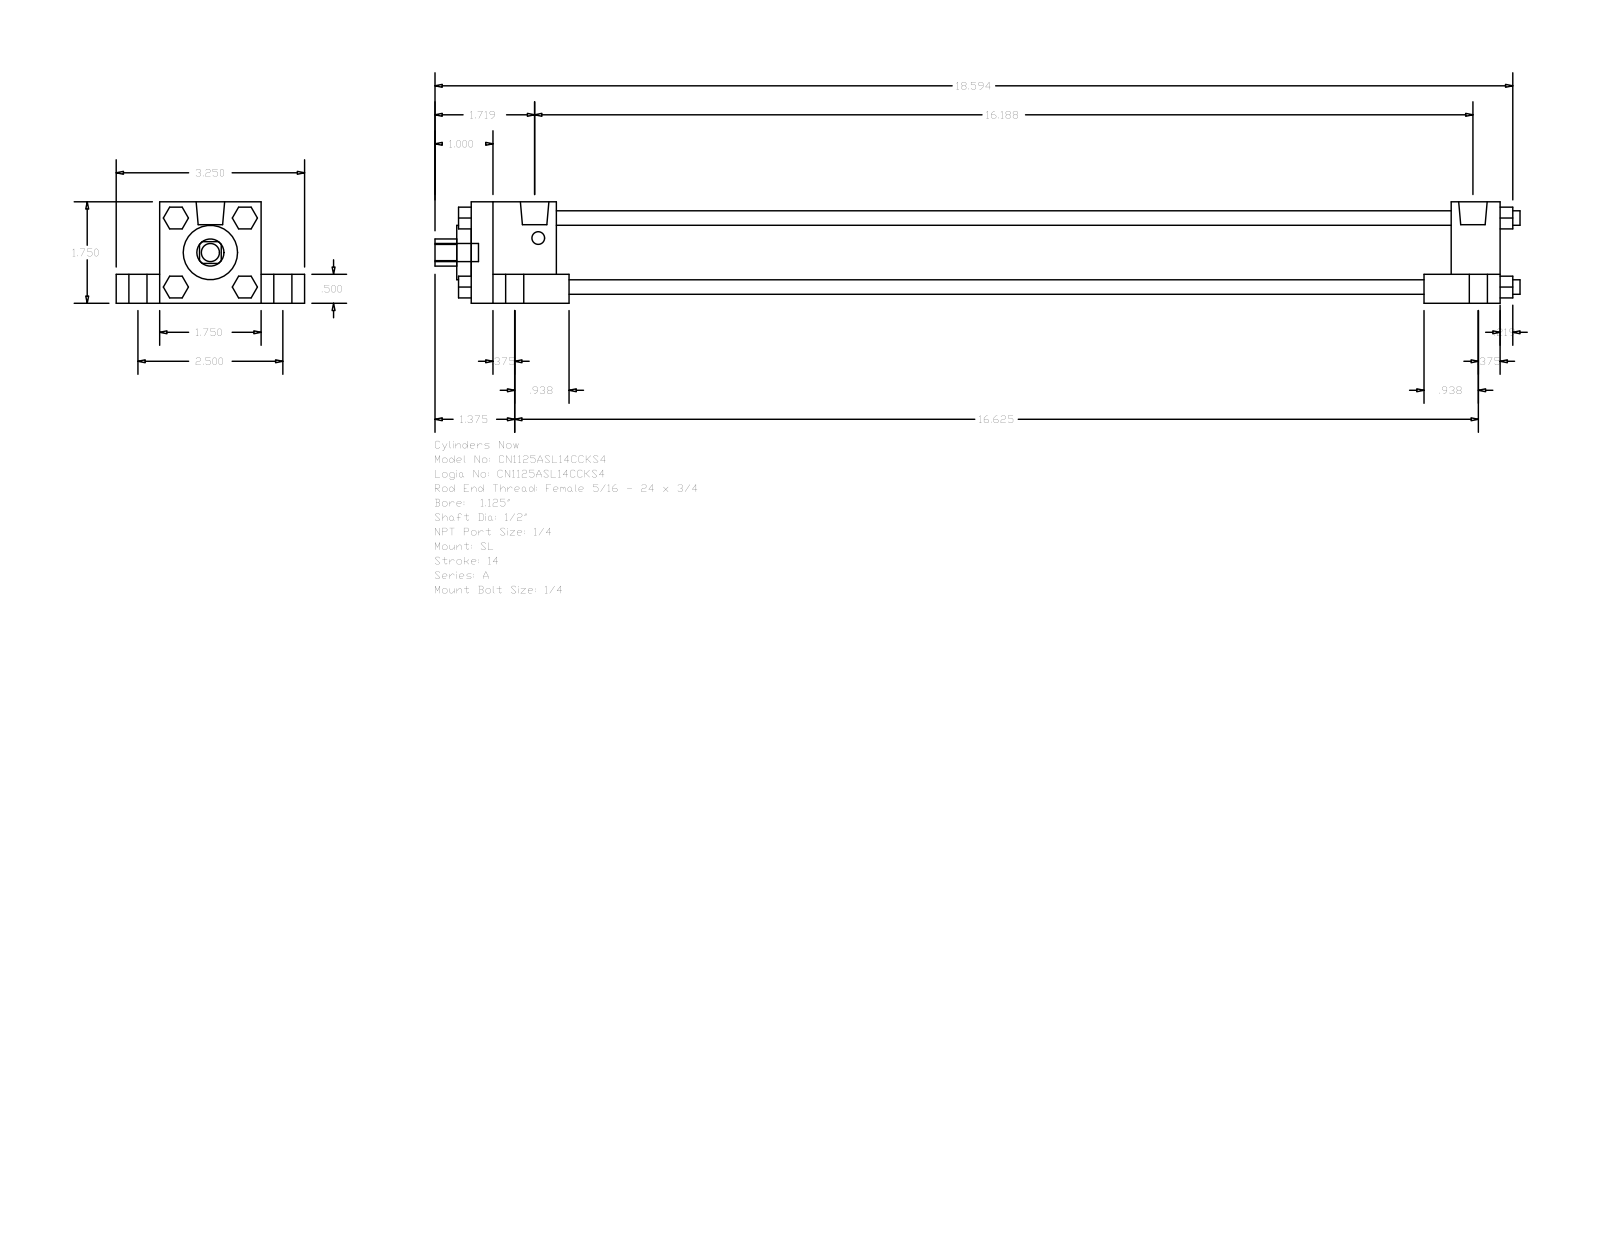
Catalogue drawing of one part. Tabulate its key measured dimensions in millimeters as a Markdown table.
| quantity | value |
| --- | --- |
| part name | A_SL__0112_0.5 |
| STEP written by | GSSL Pune (CONFIG_CONTROL_DESIGN) |
| units | millimeters |
| bodies | 0 solids, 150 faces (114 planar, 36 cylindrical, 0 other) |
| overall size | 475.46 × 82.55 × 44.45 |
| round holes (diameter × count) | 12.7 × 1, 23.81 × 1, 31.88 × 1 |
| round bosses / shafts (diameter × count) | 7.94 × 5, 14.29 × 4, 6.35 × 4, 5.56 × 4, 12.49 × 2 |
| partial cylindrical surfaces (radius × count) | 5.94 × 1 |
| main face-to-face distances | 44.46, 31.76, 12.7, 19.04, 63.5, 450.85, 429.41, 21.44, 37.3, 392.11 |
